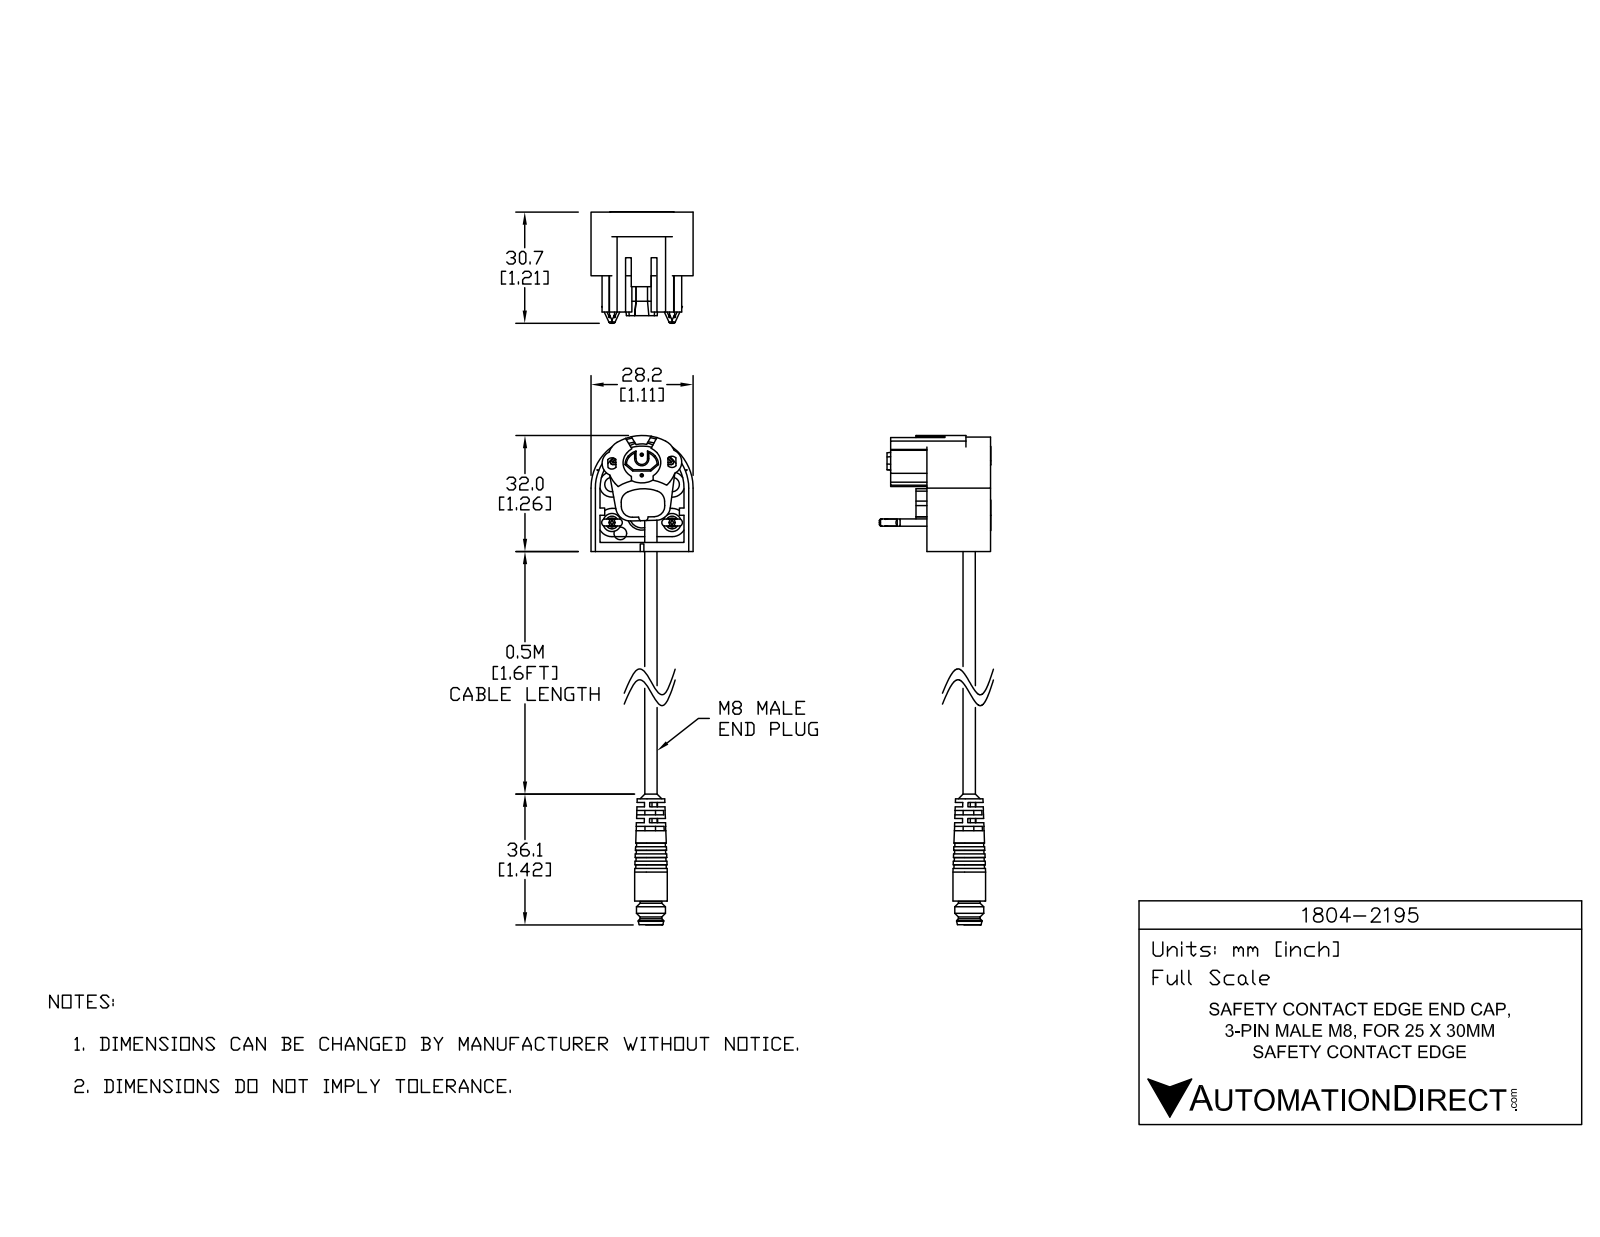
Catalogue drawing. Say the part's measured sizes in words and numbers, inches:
The part is named "1804-2195_a". Its 3-D file was written by "SolidWorks 2018 (AUTOMOTIVE_DESIGN)". It is 6 solids with 386 faces: 196 planar, 123 cylindrical and 67 other. Overall it measures 5.519 by 1.213 by 1.11 inches. Its volume is 0.727 cubic inches and its surface area 20.22 square inches. Round holes: 4 of diameter 0.02, 3 of diameter 0.138, 2 of diameter 0.035, 2 of diameter 0.059, 2 of diameter 0.122, 2 of diameter 0.157, 2 of diameter 0.217, 1 of diameter 0.134, 1 of diameter 0.228. Round bosses or shafts: 3 of diameter 0.039, 2 of diameter 0.236, 2 of diameter 0.197, 2 of diameter 0.138, 2 of diameter 0.098, 2 of diameter 0.079, 2 of diameter 0.028, 1 of diameter 0.346. Partial cylindrical surfaces (rounded edges, fillets, slot ends): 8 of radius 0.039, 6 of radius 0.118, 6 of radius 0.138, 4 of radius 0.157, 4 of radius 0.197, 2 of radius 0.154, 2 of radius 0.161, 2 of radius 0.201. The main face-to-face distances are 0.071, 0.039, 0.098, 0.031, 0.425, 1.11, 0.047, 0.228, 0.051, 0.457. The hole center spacings are 0.654, 0.055, 0.348, 0.95, 0.977, 0.099, 0.1, 0.224.
